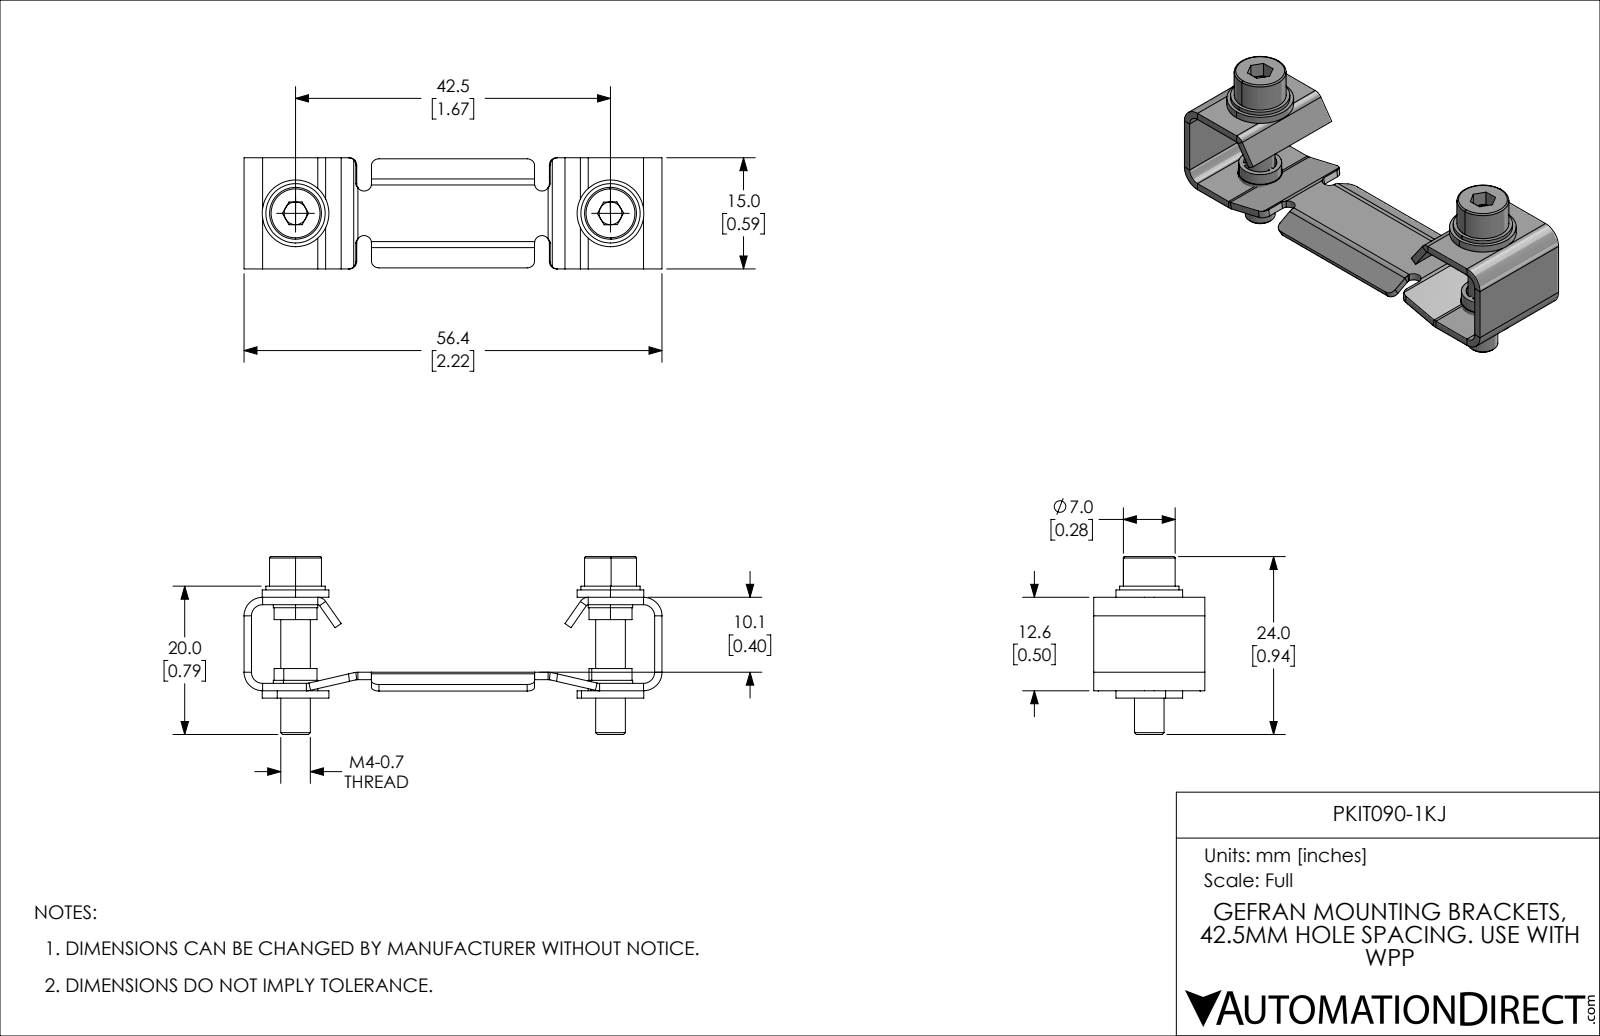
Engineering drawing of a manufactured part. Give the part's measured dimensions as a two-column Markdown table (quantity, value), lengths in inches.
| quantity | value |
| --- | --- |
| part name | PKIT090-1KJ |
| STEP written by | SolidWorks 2021 (CONFIG_CONTROL_DESIGN) |
| units | inches |
| bodies | 9 solids, 343 faces (172 planar, 111 cylindrical, 60 other) |
| overall size | 2.22 × 0.945 × 0.591 |
| volume | 0.155 in³ |
| surface area | 7.989 in² |
| round holes (diameter × count) | 0.169 × 2, 0.177 × 2, 0.232 × 2 |
| round bosses / shafts (diameter × count) | 0.354 × 2, 0.315 × 2, 0.276 × 2, 0.236 × 2, 0.228 × 2, 0.157 × 2 |
| partial cylindrical surfaces (radius × count) | 0.014 × 12, 0.039 × 12, 0.059 × 8, 0.098 × 8, 0.012 × 2, 0.029 × 2, 0.051 × 2, 0.069 × 2 |
| main face-to-face distances | 0.039, 0.496, 0.059, 0.457, 0.098, 0.437, 0.398, 0.079, 0.02, 0.535 |
| hole center spacings | 1.673 |
